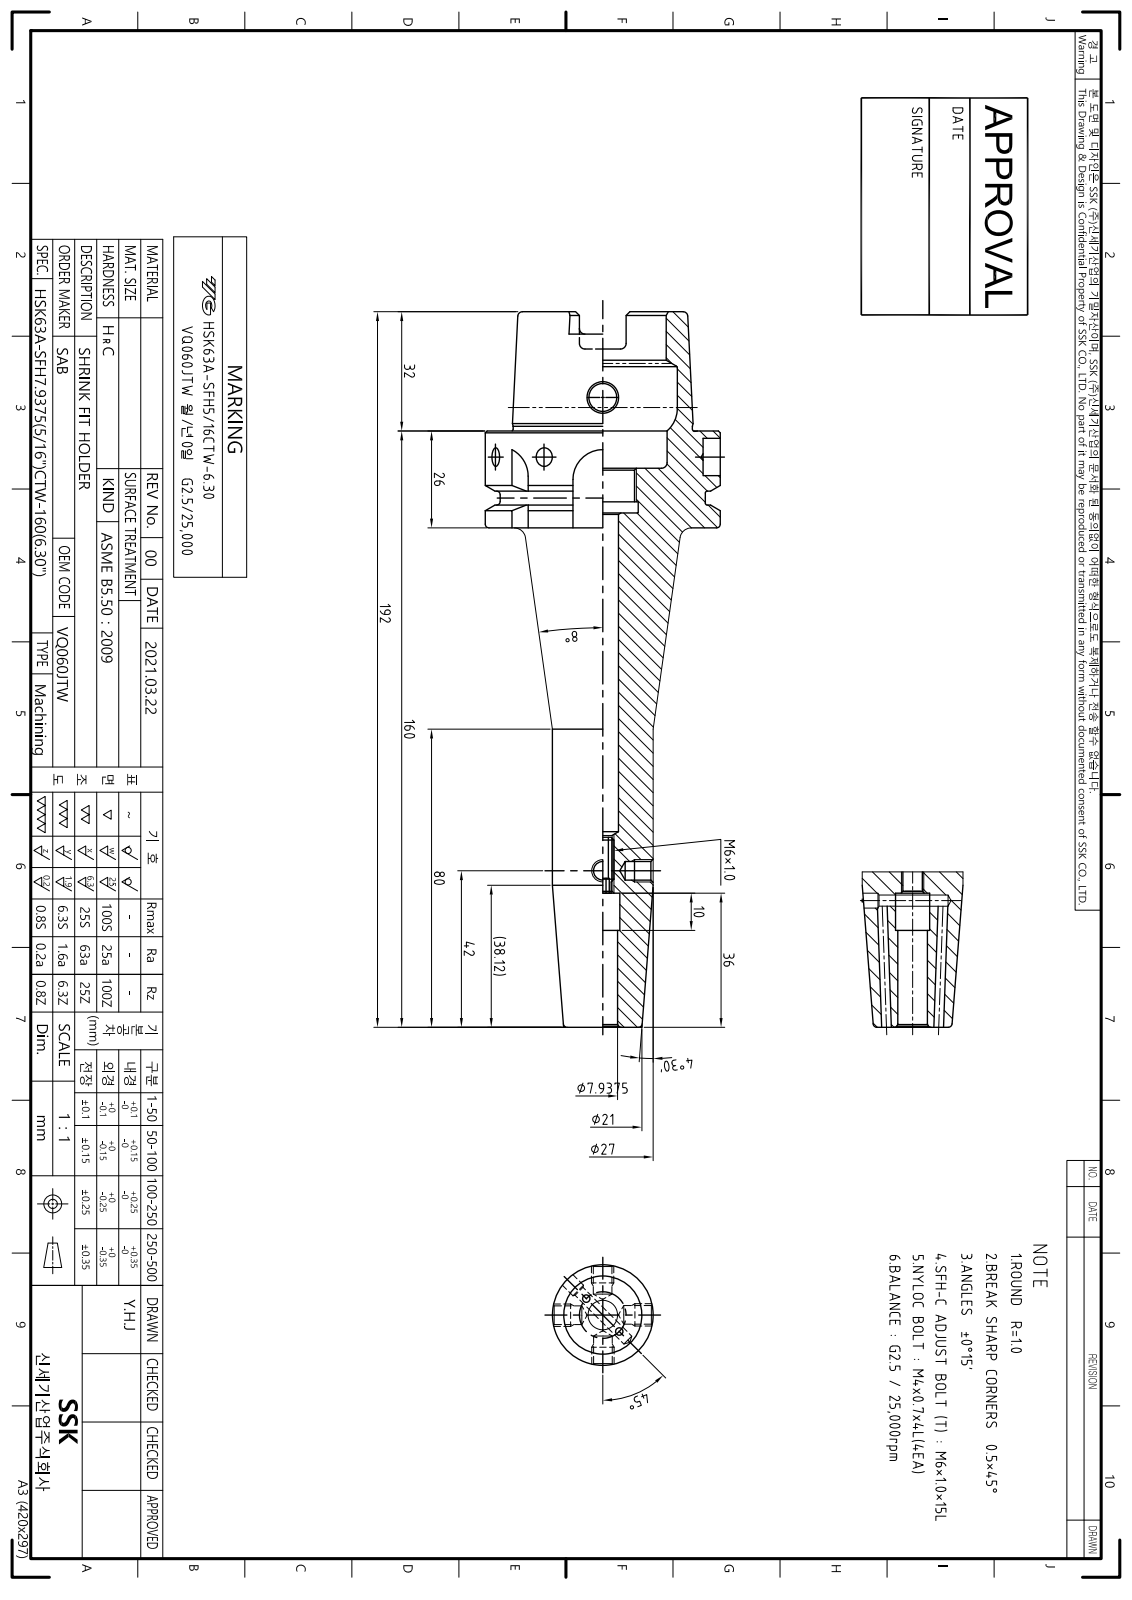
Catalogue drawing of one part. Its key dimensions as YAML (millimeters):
part_name: "LO-HSK63A-SFH7.9375CTW-160"
step_written_by: "Autodesk Inventor 2022 (AUTOMOTIVE_DESIGN)"
units: millimeters
bodies: {solids: 1, faces: 120, planar: 42, cylindrical: 36, other: 42}
overall_size: [192, 63, 63]
volume: 167880
surface_area: 37467
round_holes:
  - {diameter: 2, count: 2}
  - {diameter: 4.3, count: 1}
  - {diameter: 7.5, count: 1}
  - {diameter: 7.94, count: 1}
  - {diameter: 8, count: 1}
  - {diameter: 9.14, count: 1}
  - {diameter: 10, count: 1}
  - {diameter: 16.92, count: 1}
  - {diameter: 19, count: 1}
  - {diameter: 34, count: 1}
  - {diameter: 40, count: 1}
round_bosses_or_shafts:
  - {diameter: 63, count: 1}
  - {diameter: 55, count: 1}
  - {diameter: 48.04, count: 1}
  - {diameter: 27, count: 1}
partial_cylinders:
  - {radius: 1.5, count: 6}
  - {radius: 2.88, count: 4}
  - {radius: 8, count: 4}
face_to_face_distances: [26, 10, 16, 32, 42, 58, 150, 160, 134, 53]
